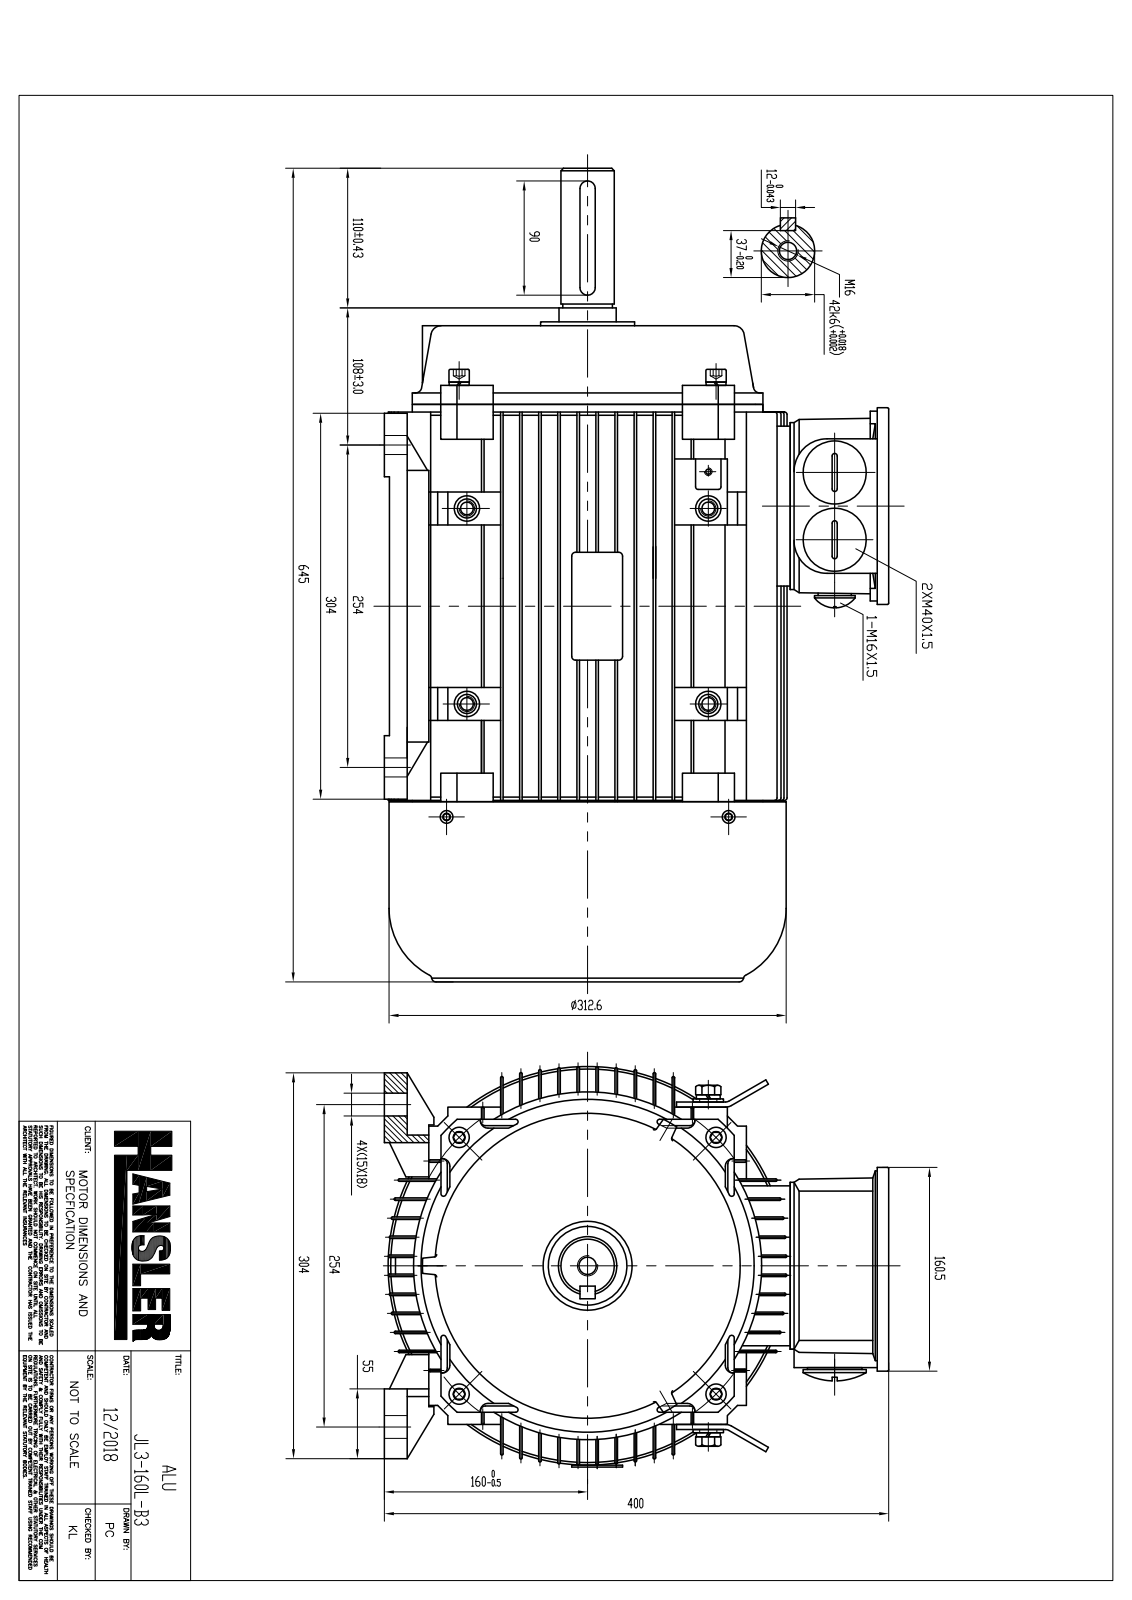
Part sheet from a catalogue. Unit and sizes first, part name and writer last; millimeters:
Units: millimetres
Overall size (bounding box): 633 × 402.7 × 316
Round holes (diameter × count): ⌀5 ×28, ⌀4.12 ×12, ⌀8.39 ×8, ⌀9.1 ×8, ⌀10 ×8, ⌀21 ×8, ⌀5.25 ×5, ⌀5.3 ×5, ⌀8 ×5, ⌀16 ×5, ⌀4.2 ×4, ⌀5.48 ×4
Round bosses / shafts (diameter × count): ⌀8 ×10, ⌀5.38 ×9, ⌀15 ×8, ⌀12.59 ×8, ⌀7.19 ×8, ⌀10 ×5, ⌀7.85 ×5, ⌀5 ×5
Partial cylindrical surfaces — rounded edges, fillets, slot ends (radius × count): R1.2 ×262, R1 ×185, R2 ×182, R1.37 ×37, R3 ×32, R1.5 ×26, R3.42 ×25, R4 ×20
Main face-to-face distances: 15, 30, 2, 45, 13, 90, 17, 75, 60, 105
Hole centre spacings: 202.36, 14.64, 202.24, 95.35, 134, 202.23, 78, 110
Volume: 7 143 000 mm³ · Surface area: 2 763 000 mm²
Bodies: 67 solids, 8550 faces (3943 planar, 2113 cylindrical, 2494 other)
Part name (STEP PRODUCT): JL3-160L-B3
STEP written by: SIEMENS PLM Software NX 10.0 (CONFIG_CONTROL_DESIGN)
